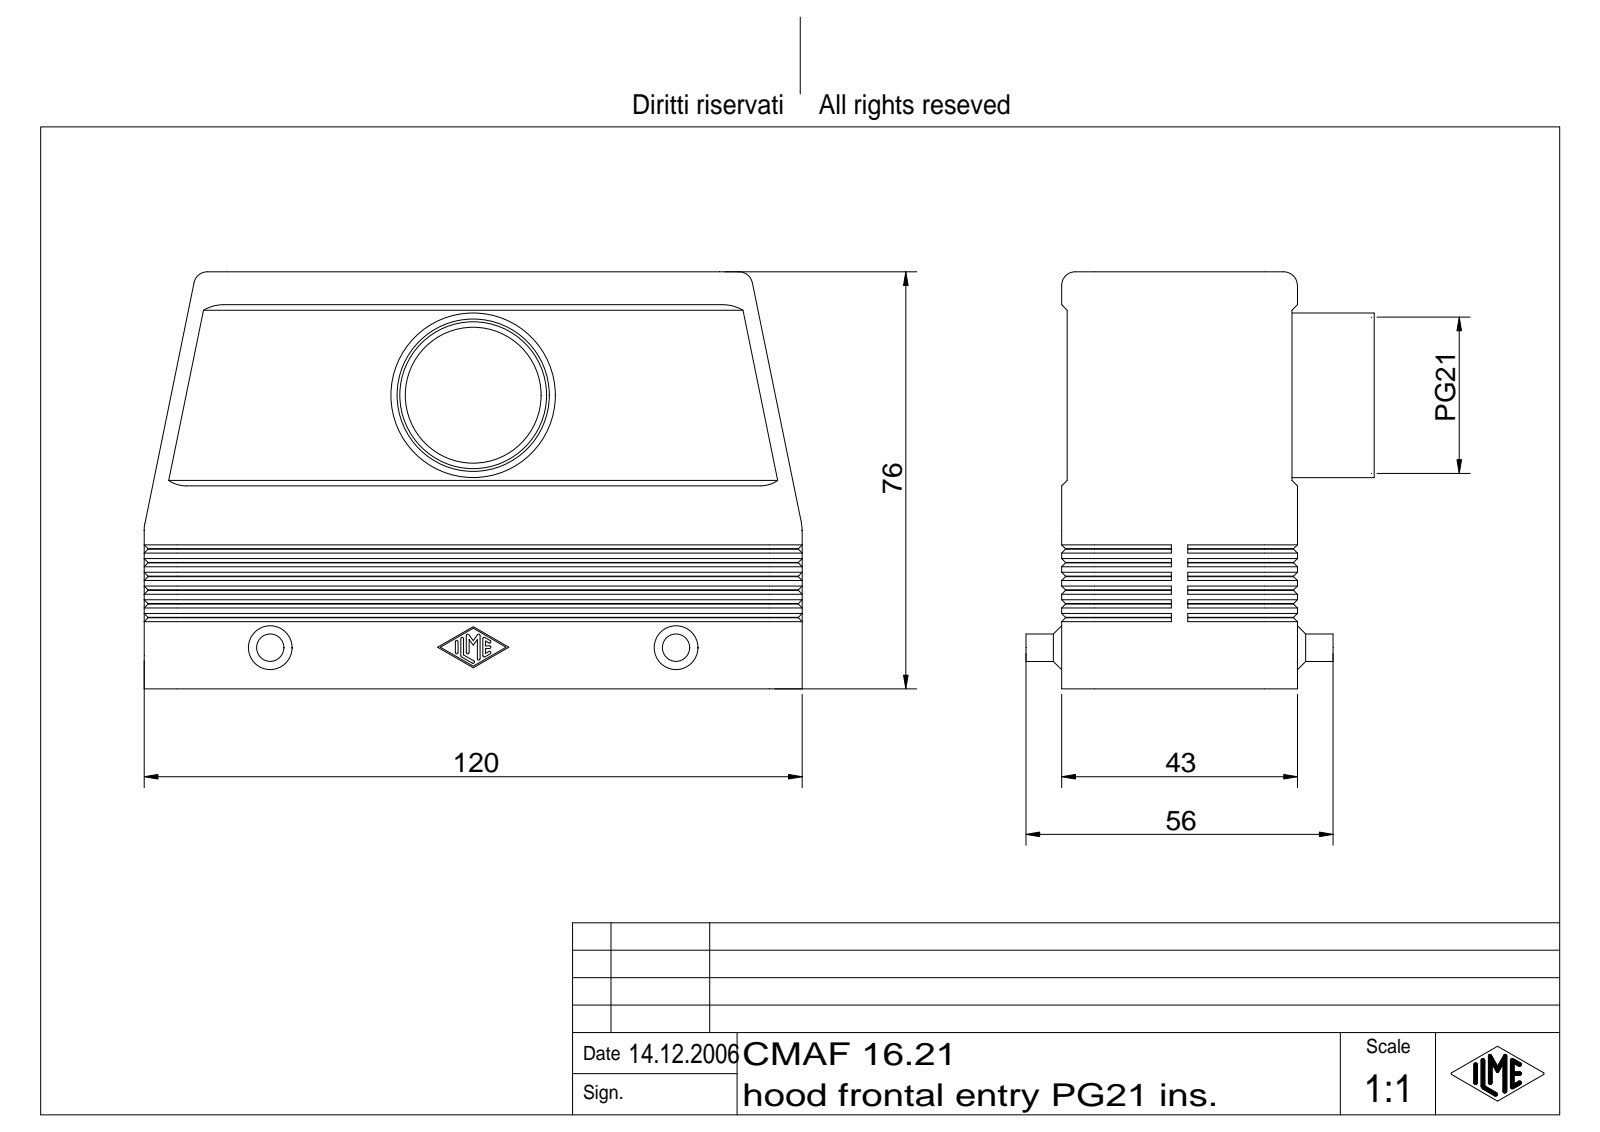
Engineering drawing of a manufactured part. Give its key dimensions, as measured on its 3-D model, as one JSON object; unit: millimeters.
{"part_name": "CAO Tüllengehäuse 2 Bügel für einen Einsatz", "step_written_by": "Autodesk Inventor 7 (AUTOMOTIVE_DESIGN)", "units": "millimeters", "bodies": {"solids": 1, "faces": 521, "planar": 195, "cylindrical": 132, "other": 194}, "overall_size": [120, 76, 63.5], "volume_mm3": 91282, "surface_area_mm2": 57525, "round_holes": [[24.78, 1], [26.78, 1]], "round_bosses_or_shafts": [[5, 2], [30, 1]], "partial_cylinders_radius": [[0.25, 14], [6, 10], [2, 4], [2.5, 4], [3, 4], [5.3, 2], [20, 1], [23, 1]], "face_to_face_distances": [3, 2, 40, 37, 39, 1, 42, 43, 41, 5]}
